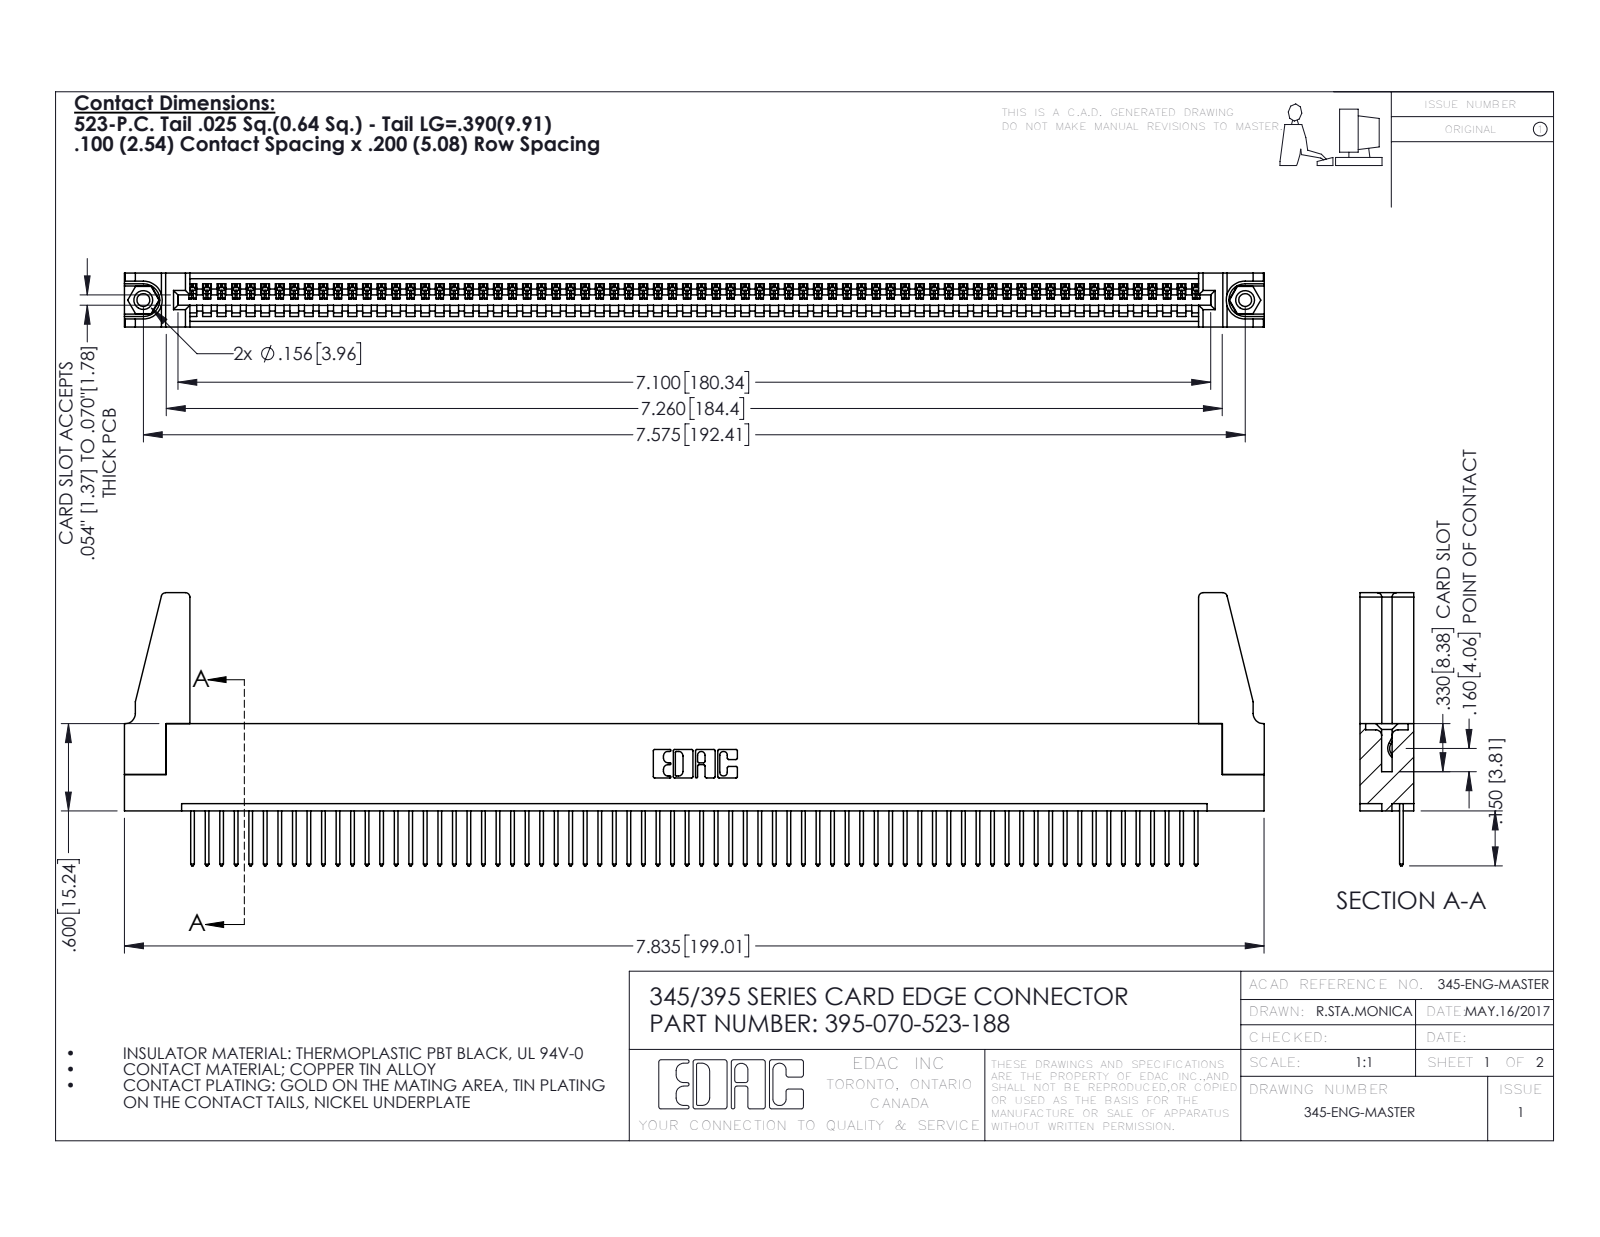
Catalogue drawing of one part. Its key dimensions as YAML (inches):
part_name: "345-250-001_345-250-001-102; 345 Part_Flush Mounting Lugs - 0.156 Dia-TH; 345-292-001_345-293-123; 345-220-078_345-220-088 (+1 more)"
step_written_by: "SolidWorks 2016 (CONFIG_CONTROL_DESIGN)"
units: inches
bodies: {solids: 75, faces: 4310, planar: 2952, cylindrical: 1342, other: 16}
overall_size: [7.836, 1.877, 0.37]
volume: 1.364
surface_area: 44.91
round_holes:
  - {diameter: 0.089, count: 2}
  - {diameter: 0.125, count: 2}
  - {diameter: 0.156, count: 2}
  - {diameter: 0.064, count: 1}
round_bosses_or_shafts:
  - {diameter: 0.155, count: 2}
partial_cylinders:
  - {radius: 0.006, count: 140}
  - {radius: 0.01, count: 140}
  - {radius: 0.01, count: 22}
  - {radius: 0.03, count: 8}
  - {radius: 0.007, count: 6}
  - {radius: 0.031, count: 6}
  - {radius: 0.026, count: 3}
  - {radius: 0.031, count: 2}
face_to_face_distances: [0.072, 0.298, 0.37, 0.2, 0.098, 0.272, 0.025, 0.225, 0.149, 0.072]
hole_center_spacings: [0.27, 7.339, 7.575]
